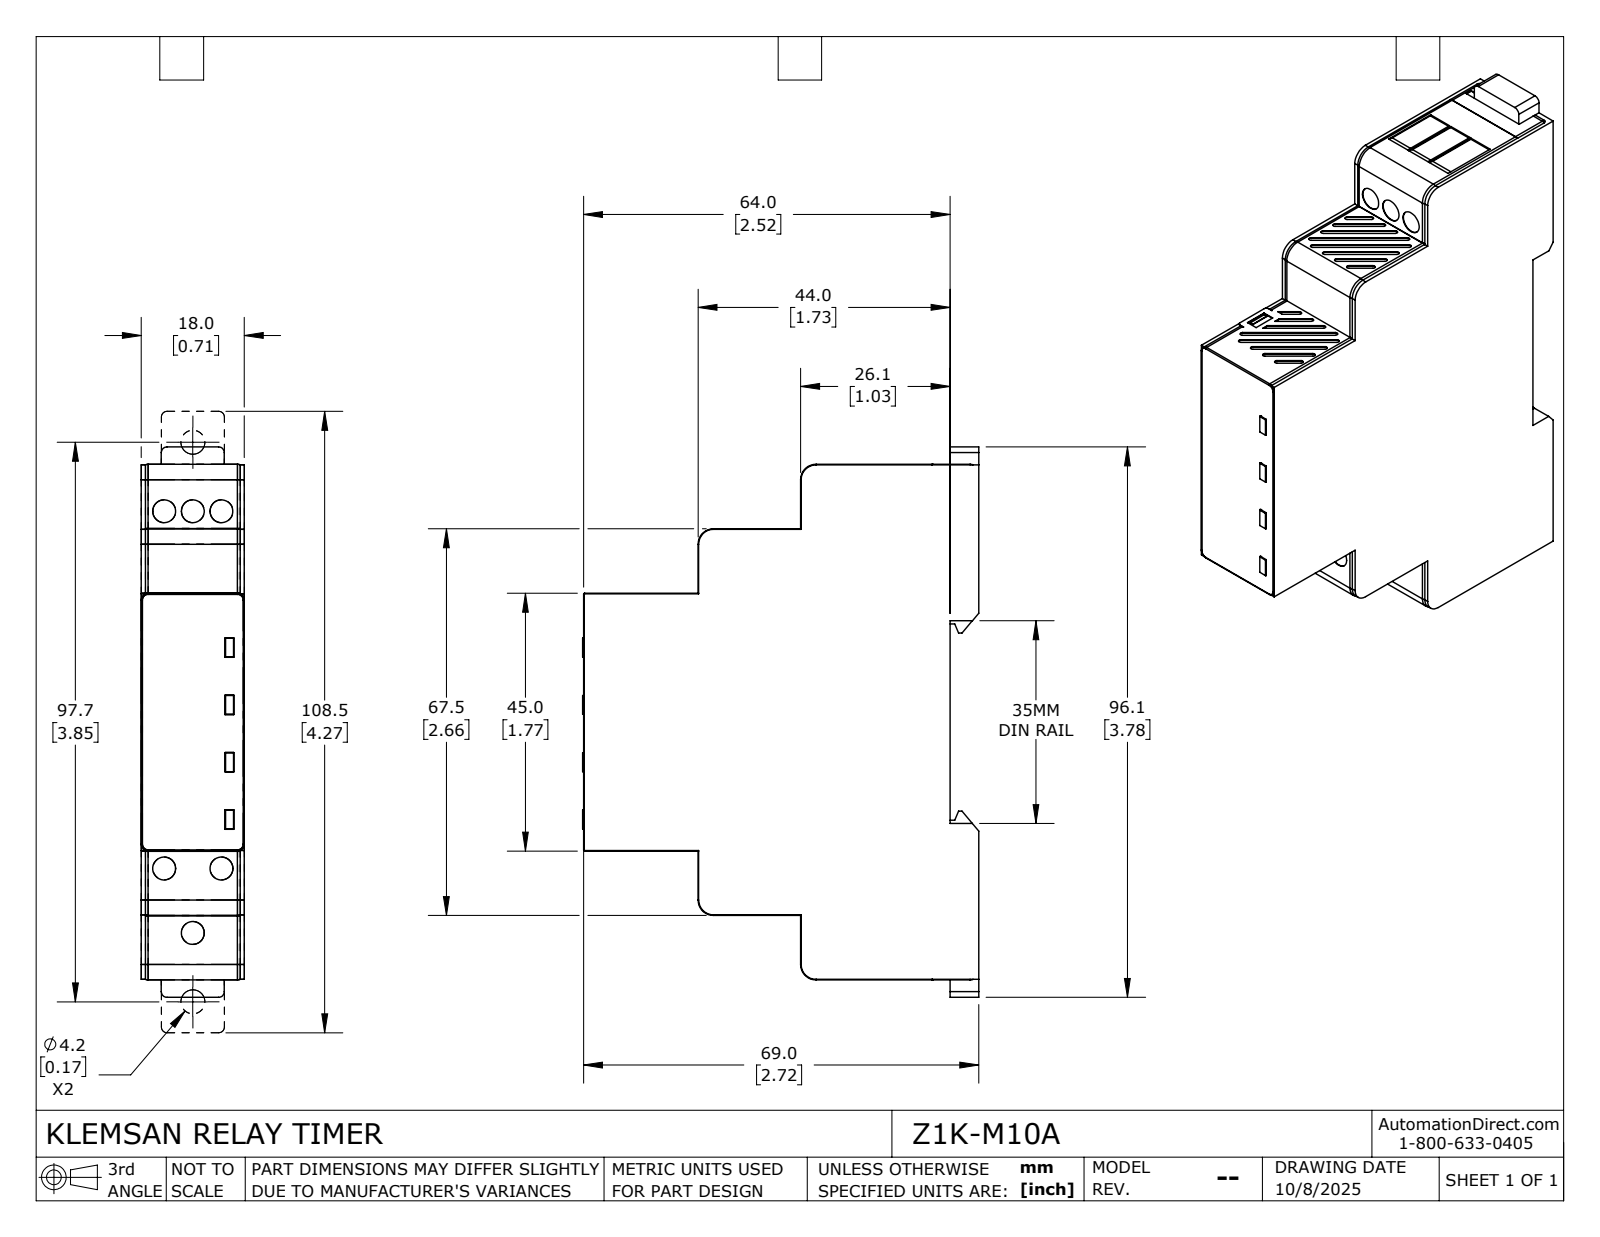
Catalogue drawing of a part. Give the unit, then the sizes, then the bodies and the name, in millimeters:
Units: millimetres
Overall size (bounding box): 96.07 × 69.15 × 18
Round holes (diameter × count): ⌀4.2 ×2, ⌀4 ×1
Partial cylindrical surfaces — rounded edges, fillets, slot ends (radius × count): R1.2 ×16, R0.2 ×4, R1 ×4, R2.6 ×4, R2.7 ×4, R0.5 ×2, R1.5 ×2
Main face-to-face distances: 18, 3.5, 14.5, 11.25, 64, 5, 69, 22.5, 67.4, 67.5
Hole centre spacings: 5.83, 79.43, 85.26
Volume: 83 847 mm³ · Surface area: 17 884 mm²
Bodies: 3 solids, 440 faces (280 planar, 60 cylindrical, 100 other)
Part name (STEP PRODUCT): Z1K-M10A
STEP written by: SolidWorks 2024 (CONFIG_CONTROL_DESIGN)
